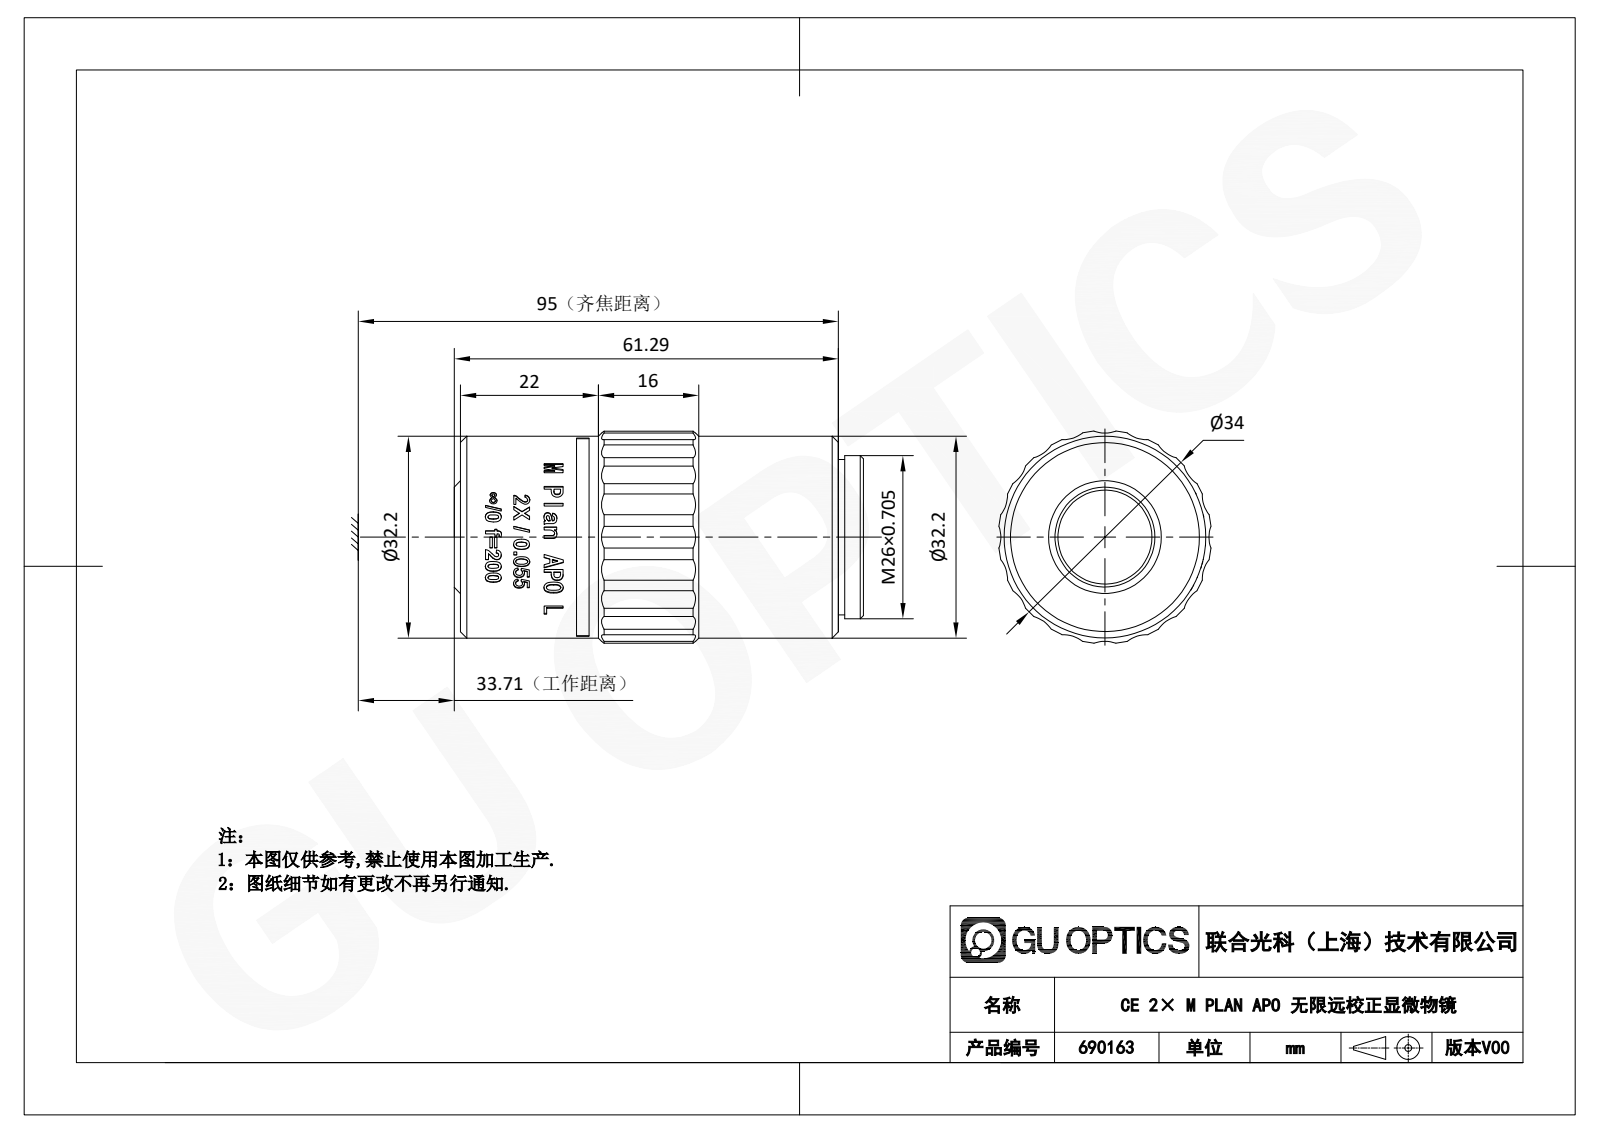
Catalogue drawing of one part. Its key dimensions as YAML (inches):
part_name: "690163"
step_written_by: "SolidWorks 2020 (CONFIG_CONTROL_DESIGN)"
units: inches
bodies: {solids: 1, faces: 379, planar: 111, cylindrical: 95, other: 173}
overall_size: [2.57, 1.331, 1.331]
volume: 3.13
surface_area: 13.11
round_holes:
  - {diameter: 0.591, count: 1}
  - {diameter: 0.866, count: 1}
round_bosses_or_shafts:
  - {diameter: 1.268, count: 1}
  - {diameter: 1.26, count: 1}
  - {diameter: 1.024, count: 1}
  - {diameter: 0.976, count: 1}
partial_cylinders:
  - {radius: 0.197, count: 20}
  - {radius: 0.626, count: 1}
  - {radius: 0.669, count: 1}
face_to_face_distances: [2.425, 2.374, 0.051, 0.02, 2.444, 2.393, 0.157, 0.106, 2.531, 2.551]
